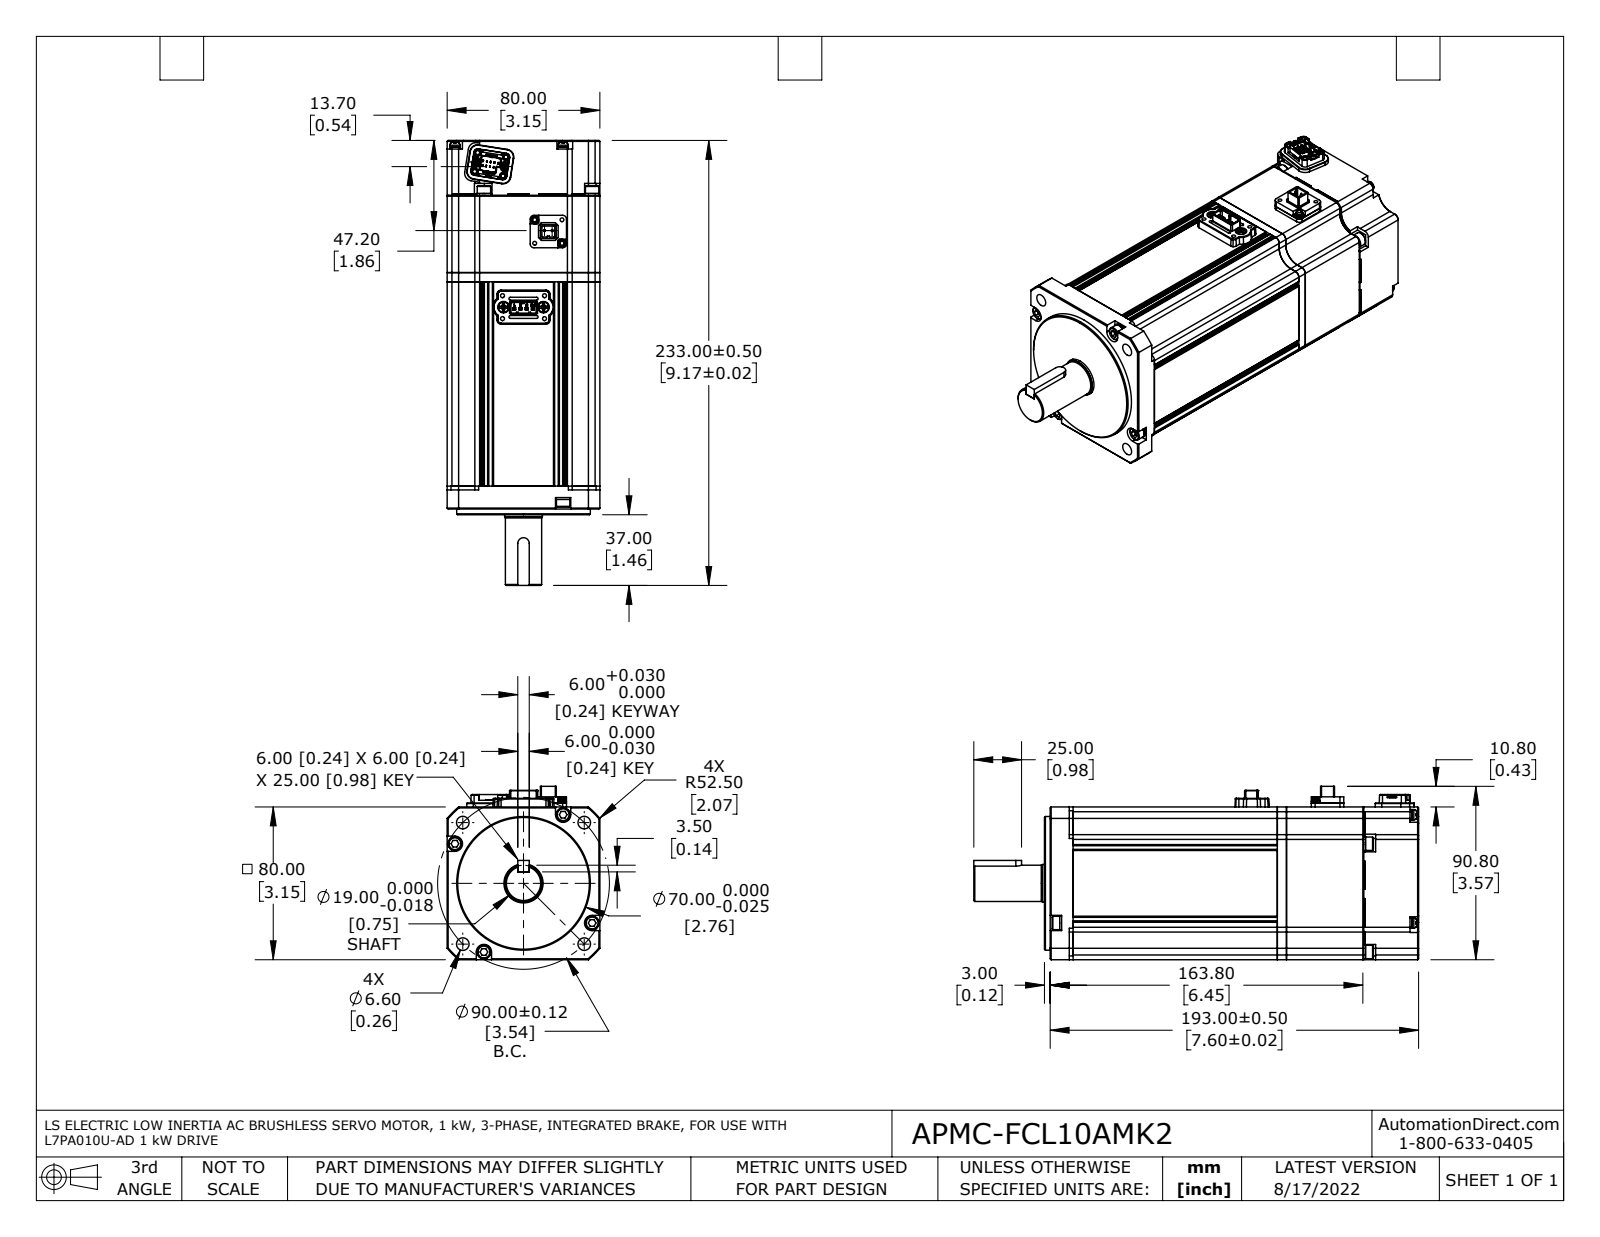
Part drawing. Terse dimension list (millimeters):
name: SLM08GA003G04_Out Line(APMC-FCL10AMK2(Ver.1.2) r1 nc fxt
written by: SolidWorks 2017 (AUTOMOTIVE_DESIGN)
unit: mm
bodies: 50 solids, 2078 faces (1312 planar, 562 cylindrical, 204 other)
size: 233 × 90.8 × 80
volume: 1 105 000 mm³; area: 155 300 mm²
holes: 10× ⌀2.1, 8× ⌀4, 8× ⌀4.5, 6× ⌀2, 6× ⌀3, 4× ⌀3.5, 4× ⌀6.6, 2× ⌀1, 2× ⌀6, 1× ⌀3.3, 1× ⌀3.4, 1× ⌀13
bosses: 8× ⌀7.2, 8× ⌀7, 6× ⌀5.4, 2× ⌀4.2, 2× ⌀3.6, 2× ⌀3.5, 2× ⌀2.2, 2× ⌀0.9
rounds: 36× R0.3, 20× R0.2, 12× R2, 10× R1, 9× R0.2, 9× R2.5, 7× R0.5, 7× R4
face distances: 80, 111.8, 4.8, 107, 46, 40.5, 45.3, 152.3, 0.7, 41.2
hole spacings: 41.5, 11.8, 52.7, 58.7, 68.7, 85.8, 6, 9.4
